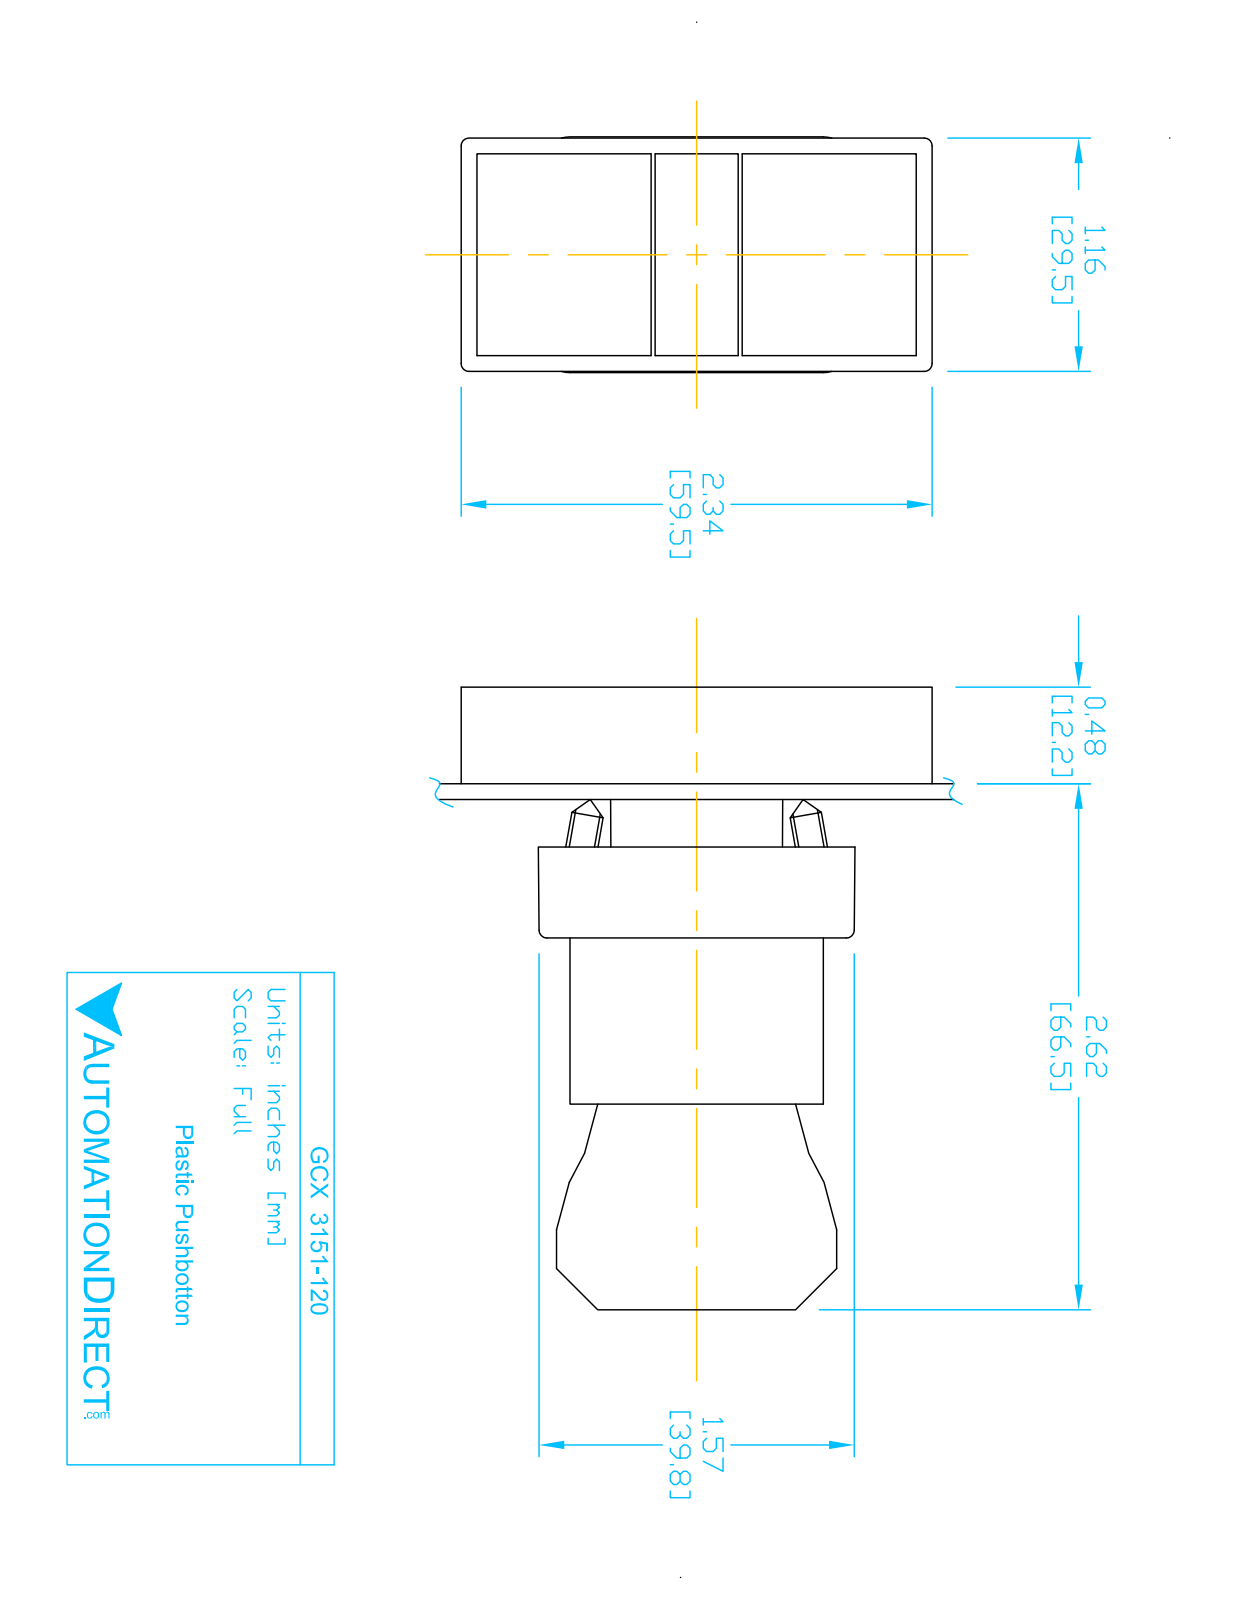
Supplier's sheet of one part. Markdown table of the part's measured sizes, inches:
| quantity | value |
| --- | --- |
| part name | ecx1030; ECX3029-2; ECX1050; ecx1040 (+2 more) |
| STEP written by | SolidWorks 2016 (AUTOMOTIVE_DESIGN) |
| units | inches |
| bodies | 9 solids, 531 faces (348 planar, 152 cylindrical, 31 other) |
| overall size | 3.043 × 2.343 × 1.177 |
| volume | 4.281 in³ |
| surface area | 55.77 in² |
| round holes (diameter × count) | 0.079 × 4, 0.087 × 2, 0.124 × 2, 0.13 × 2, 0.197 × 1, 0.469 × 1, 0.878 × 1, 0.888 × 1 |
| round bosses / shafts (diameter × count) | 0.157 × 4, 0.945 × 1, 0.856 × 1, 0.78 × 1, 0.504 × 1 |
| partial cylindrical surfaces (radius × count) | 0.059 × 24, 0.041 × 12, 0.124 × 12, 0.157 × 12, 0.039 × 8, 0.063 × 2, 0.079 × 2, 0.128 × 2 |
| main face-to-face distances | 0.039, 0.059, 0.02, 0.453, 0.579, 0.593, 0.74, 1.193, 0.827, 1.567 |
| hole center spacings | 0.236, 1.003, 0.974, 0.472, 0.539, 0.544, 1.083, 0.484 |
